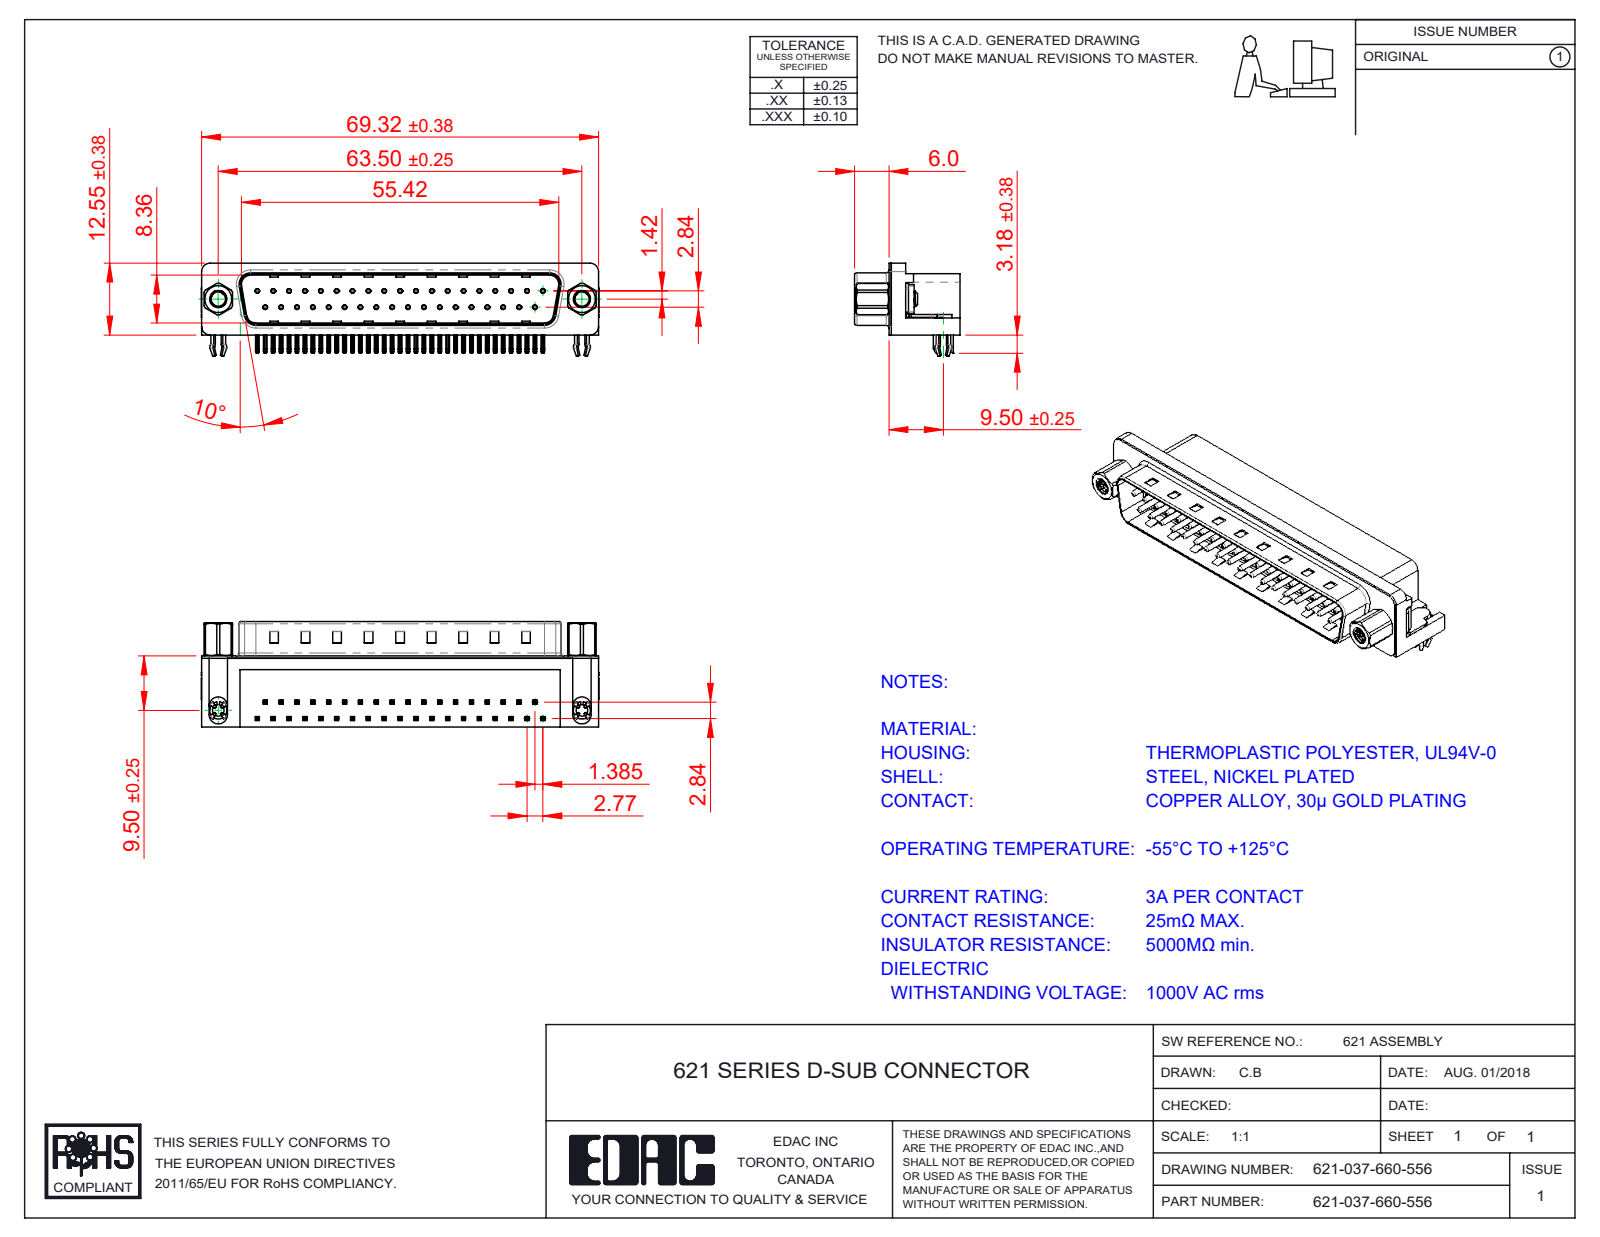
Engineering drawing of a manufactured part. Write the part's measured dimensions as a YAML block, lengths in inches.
part_name: "621-037-660-556; 621 M3 Threaded Rivet; 621 4-40 Threaded Board Mount; 621 M3 Hex Standoff 5 (+4 more)"
step_written_by: "SolidWorks 2016 (CONFIG_CONTROL_DESIGN)"
units: inches
bodies: {solids: 45, faces: 3377, planar: 2035, cylindrical: 1023, other: 319}
overall_size: [2.732, 0.724, 0.619]
volume: 0.541
surface_area: 16.59
round_holes:
  - {diameter: 0.014, count: 37}
  - {diameter: 0.031, count: 37}
  - {diameter: 0.089, count: 2}
  - {diameter: 0.098, count: 2}
  - {diameter: 0.157, count: 2}
  - {diameter: 0.189, count: 2}
  - {diameter: 0.197, count: 2}
round_bosses_or_shafts:
  - {diameter: 0.03, count: 37}
  - {diameter: 0.193, count: 2}
  - {diameter: 0.187, count: 2}
  - {diameter: 0.154, count: 2}
  - {diameter: 0.128, count: 2}
  - {diameter: 0.118, count: 2}
partial_cylinders:
  - {radius: 0.01, count: 156}
  - {radius: 0.005, count: 74}
  - {radius: 0.039, count: 16}
  - {radius: 0.02, count: 9}
  - {radius: 0.063, count: 8}
  - {radius: 0.059, count: 7}
  - {radius: 0.035, count: 4}
  - {radius: 0.079, count: 4}
face_to_face_distances: [0.016, 0.472, 0.407, 0.345, 0.083, 0.067, 0.412, 0.428, 0.354, 0.488]
hole_center_spacings: [0.124, 0.109, 0.218, 0.327, 0.436, 0.545, 0.763, 0.872]
